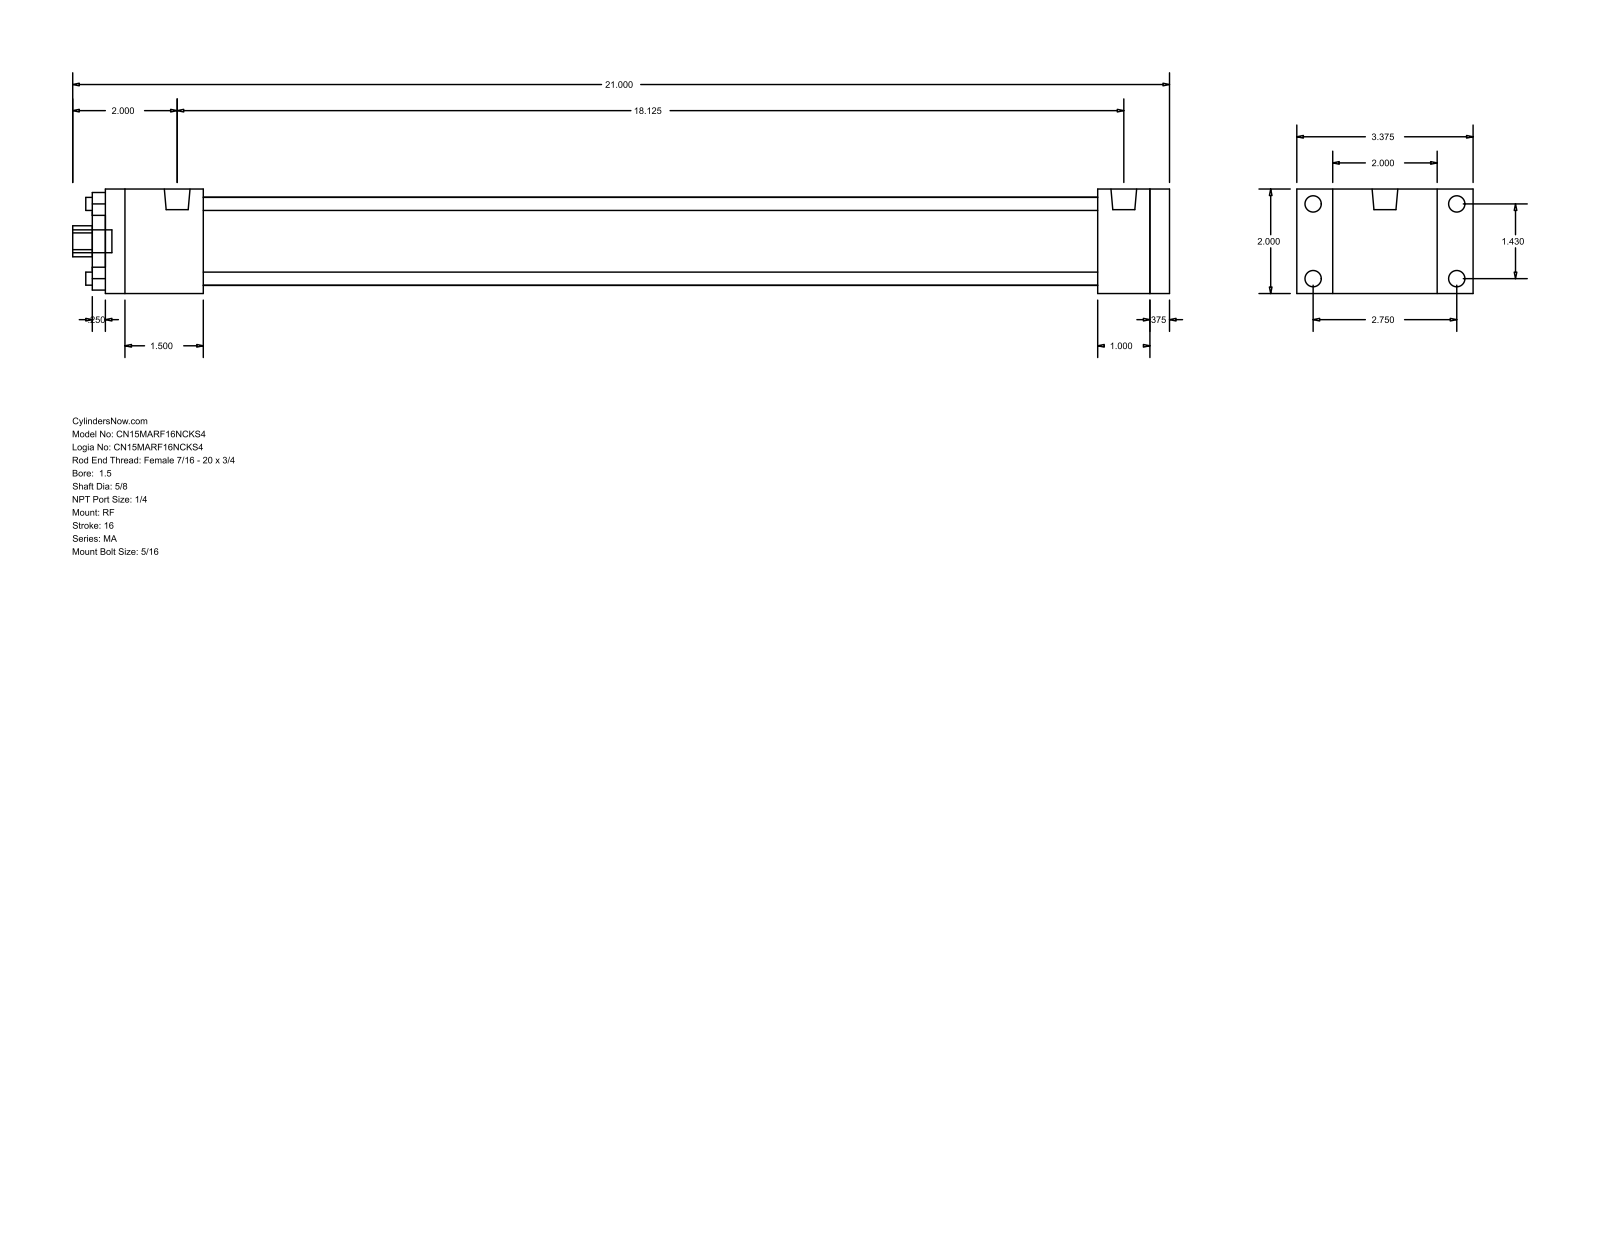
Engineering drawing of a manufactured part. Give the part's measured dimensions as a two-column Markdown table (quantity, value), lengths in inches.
| quantity | value |
| --- | --- |
| part name | MA_RF__0150_0.625 |
| STEP written by | GSSL Pune (CONFIG_CONTROL_DESIGN) |
| units | inches |
| bodies | 0 solids, 92 faces (64 planar, 28 cylindrical, 0 other) |
| overall size | 21 × 3.375 × 2 |
| round holes (diameter × count) | 0.25 × 4, 0.625 × 1, 1.125 × 1, 1.69 × 1 |
| round bosses / shafts (diameter × count) | 0.313 × 8, 0.492 × 2, 0.437 × 1 |
| partial cylindrical surfaces (radius × count) | 0.297 × 1 |
| main face-to-face distances | 2, 0.375, 20, 20.375, 19, 1, 1.375, 1.875, 17.125, 18.125 |
| hole center spacings | 1.011, 1.43, 2.022 |
